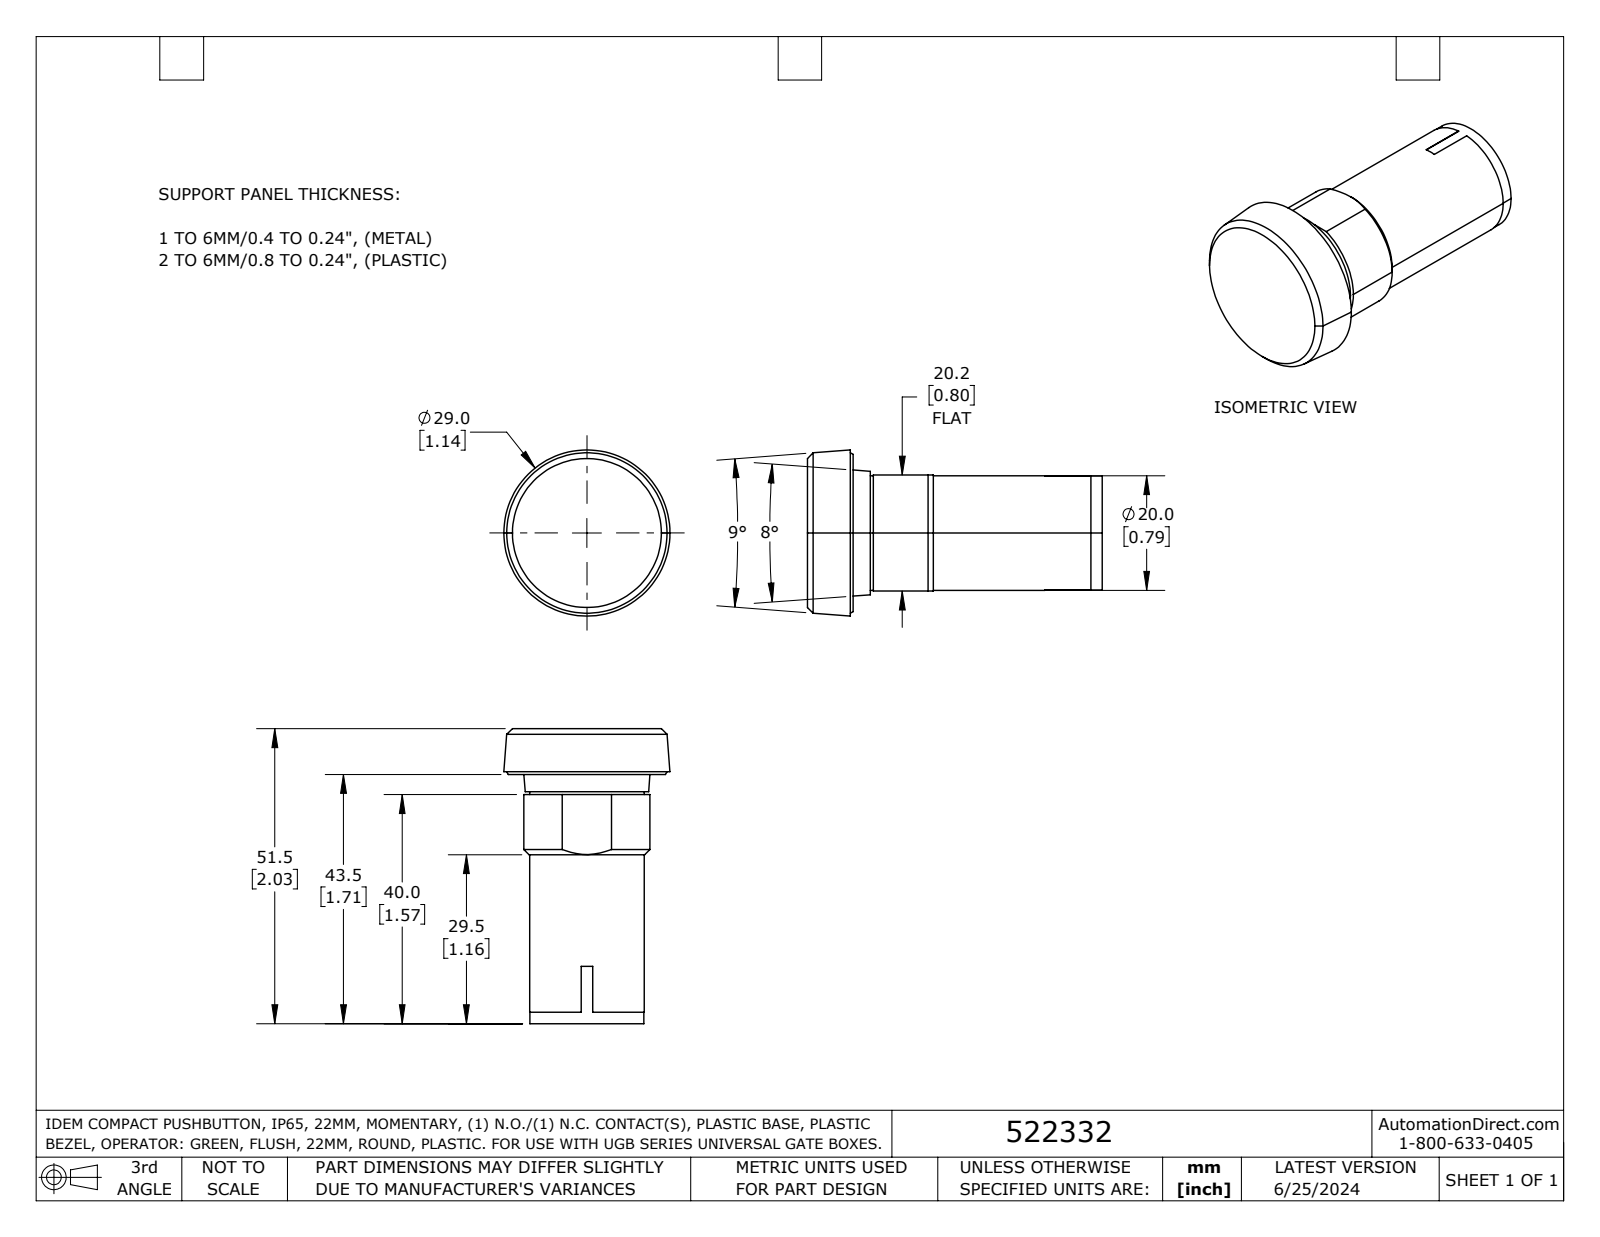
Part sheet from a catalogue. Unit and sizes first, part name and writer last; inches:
Units: inches
Overall size (bounding box): 2.028 × 1.142 × 1.142
Round bosses / shafts (diameter × count): ⌀0.787 ×1, ⌀0.783 ×1
Partial cylindrical surfaces — rounded edges, fillets, slot ends (radius × count): R0.433 ×1
Main face-to-face distances: 2.028, 0.315, 1.713, 0.138, 0.02, 0.797, 0.433, 0.453, 1.575, 0.118
Volume: 1.185 in³ · Surface area: 7.436 in²
Bodies: 1 solid, 37 faces (17 planar, 10 cylindrical, 10 other)
Part name (STEP PRODUCT): 522332
STEP written by: SolidWorks 2023 (AUTOMOTIVE_DESIGN)
